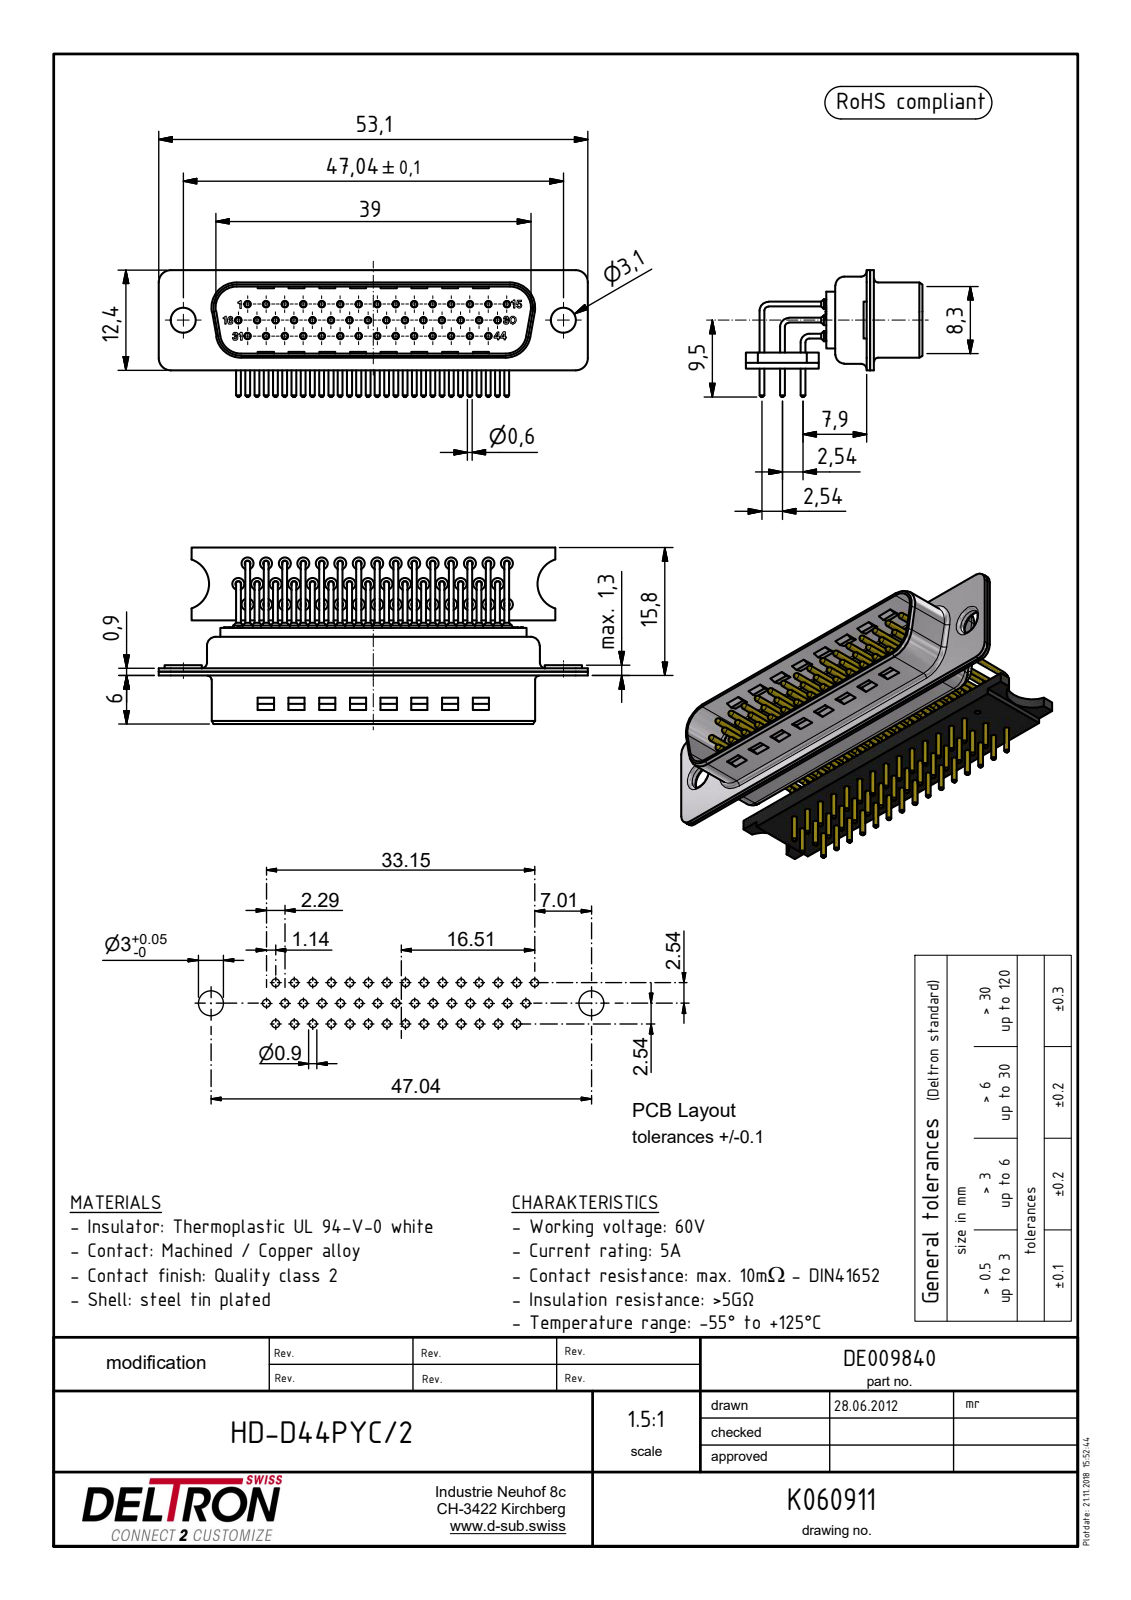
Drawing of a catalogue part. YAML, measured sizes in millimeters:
part_name: "N00787_China_BG; R+B00746_BG; R+B00745_BG; R+B00744_BG (+4 more)"
step_written_by: "Autodesk Inventor 2015 (AUTOMOTIVE_DESIGN)"
units: millimeters
bodies: {solids: 48, faces: 1375, planar: 601, cylindrical: 485, other: 289}
overall_size: [53.1, 21.84, 15.7]
volume: 3526
surface_area: 9351
round_holes:
  - {diameter: 0.7, count: 45}
  - {diameter: 0.8, count: 44}
  - {diameter: 1.26, count: 44}
  - {diameter: 1.6, count: 44}
  - {diameter: 0.34, count: 2}
  - {diameter: 3.1, count: 2}
  - {diameter: 4.06, count: 2}
round_bosses_or_shafts:
  - {diameter: 0.6, count: 88}
  - {diameter: 1.24, count: 44}
  - {diameter: 0.75, count: 44}
  - {diameter: 4.6, count: 2}
  - {diameter: 3.9, count: 2}
partial_cylinders:
  - {radius: 0.25, count: 8}
  - {radius: 0.7, count: 8}
  - {radius: 1.1, count: 8}
  - {radius: 1.5, count: 8}
  - {radius: 2, count: 8}
  - {radius: 1.3, count: 6}
  - {radius: 0.5, count: 4}
  - {radius: 1, count: 4}
face_to_face_distances: [0.5, 2, 0.4, 0.75, 9.55, 8.8, 1.5, 1.1, 0.65, 8.15]
hole_center_spacings: [2.29, 4.58, 6.87, 9.16, 11.45, 13.74, 16.03, 2.78]
